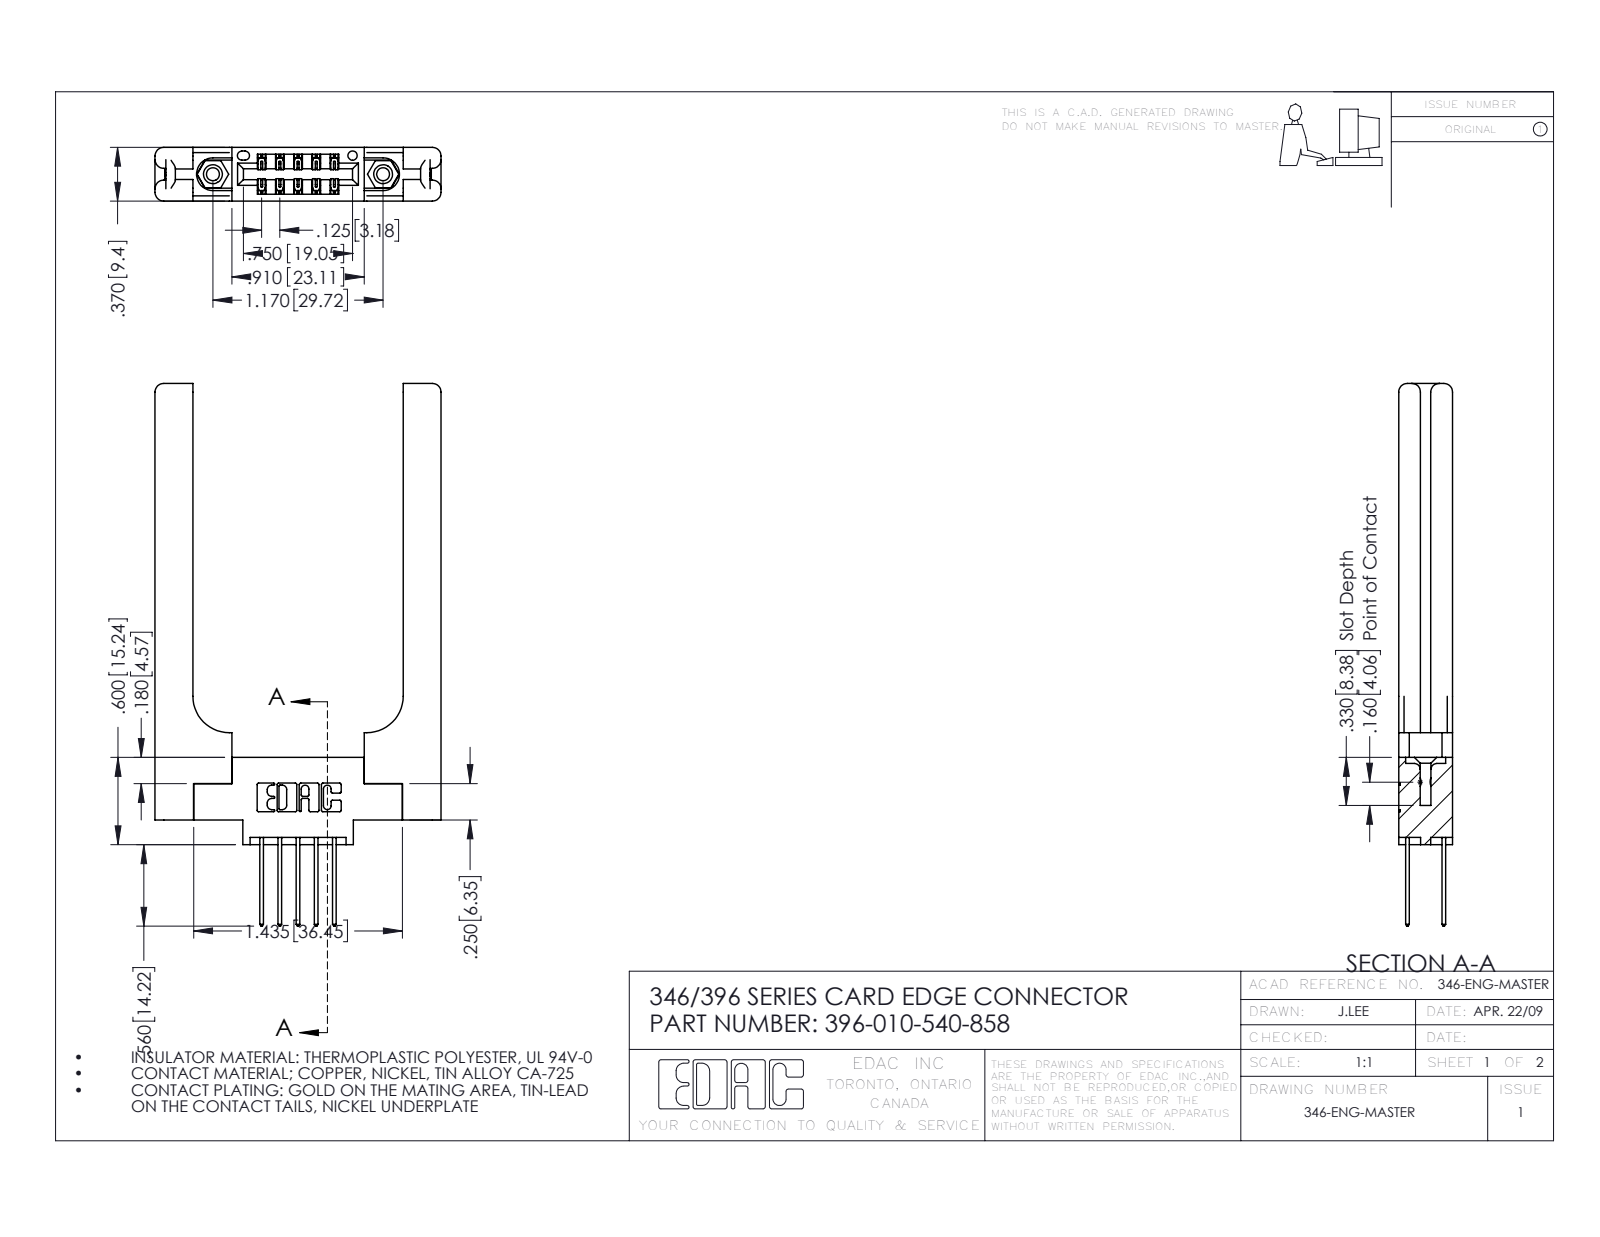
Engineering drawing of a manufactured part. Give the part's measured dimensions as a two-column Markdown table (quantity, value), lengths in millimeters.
| quantity | value |
| --- | --- |
| part name | 346 Part_0.170 Offset - 0.156 Dia-TH; 345-250-001_345-250-001-102; 346-220-058_345-220-058; 396-010-540-858 (+1 more) |
| STEP written by | SolidWorks 2016 (CONFIG_CONTROL_DESIGN) |
| units | millimeters |
| bodies | 15 solids, 902 faces (578 planar, 264 cylindrical, 60 other) |
| overall size | 94.7 × 49.9 × 9.4 |
| volume | 12 000 mm³ |
| surface area | 10 890 mm² |
| round holes (diameter × count) | 2.3 × 2, 3.2 × 2, 4 × 2, 1.6 × 1 |
| round bosses / shafts (diameter × count) | 3.9 × 2 |
| partial cylindrical surfaces (radius × count) | 0.3 × 22, 1.5 × 16, 0.2 × 15, 0.3 × 10, 0.2 × 6, 0.8 × 6, 0.7 × 3, 0.4 × 2 |
| main face-to-face distances | 9.4, 3.8, 5.6, 6.4, 1.8, 3.8, 36.7, 2.6, 1.2, 8.2 |
| hole center spacings | 6.2, 24.6, 29.7 |
